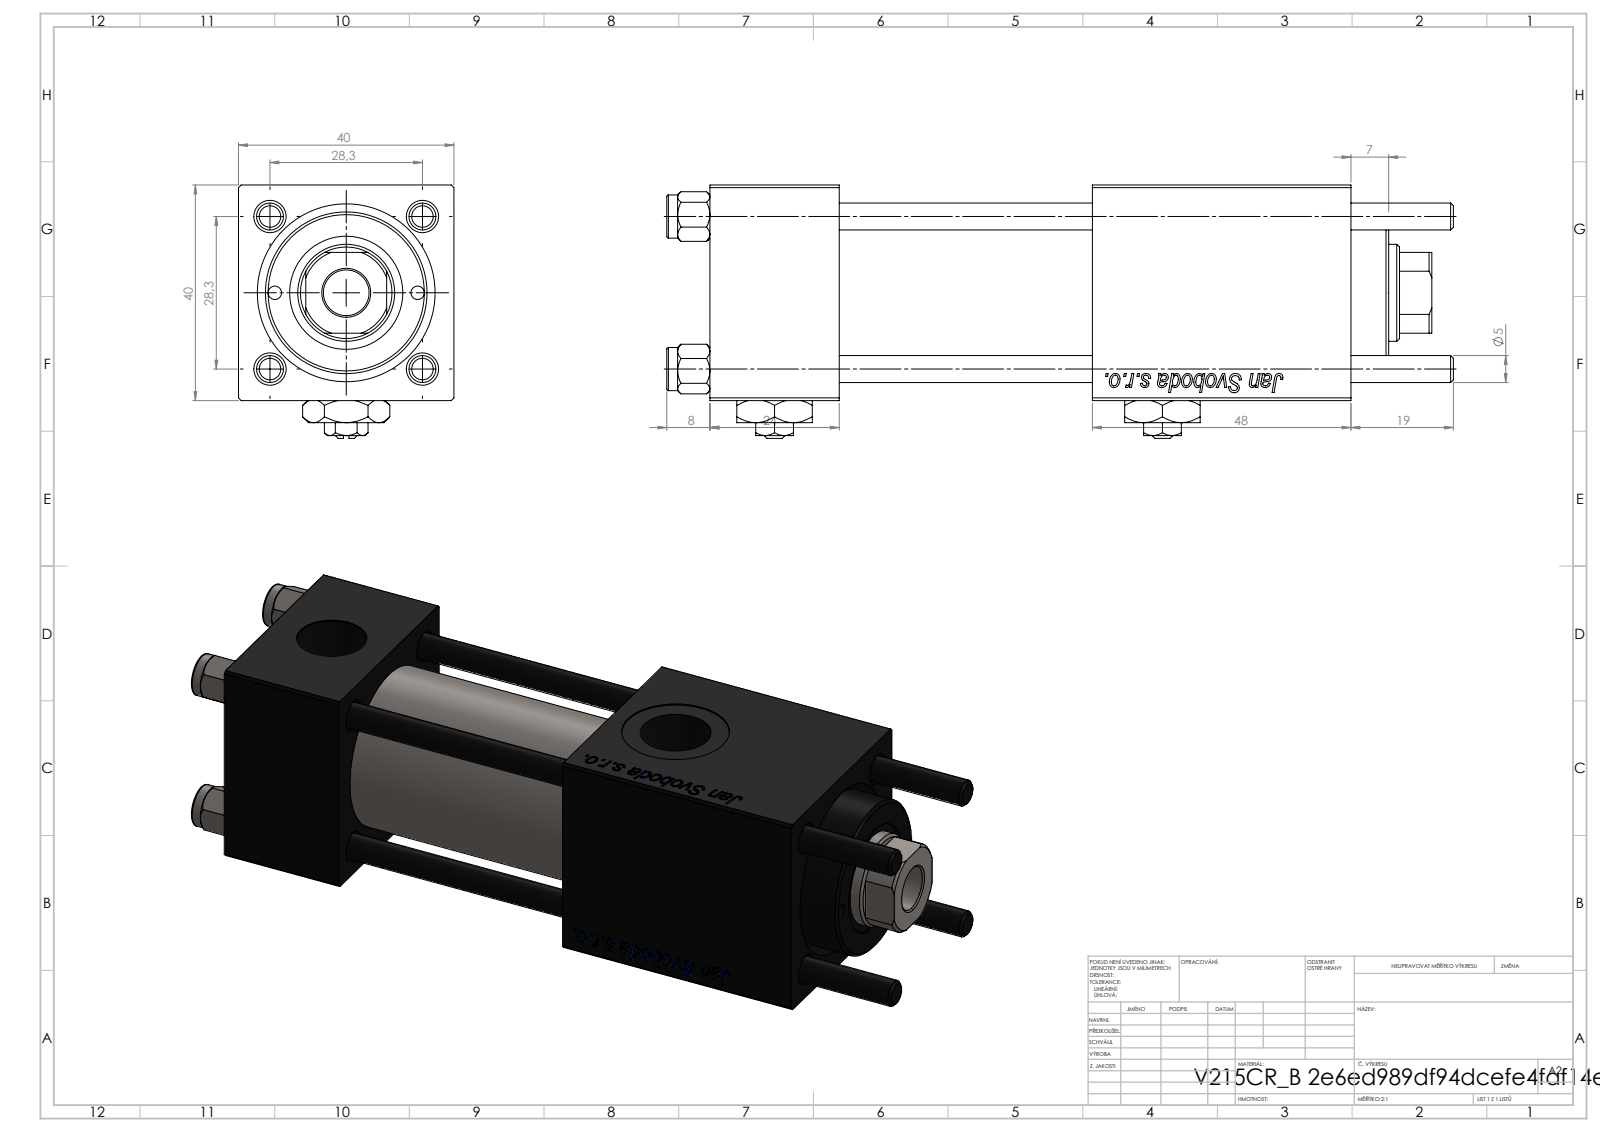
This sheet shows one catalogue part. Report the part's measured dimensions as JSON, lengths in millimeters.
{"part_name": "V215_VC_A; Zatka_pro_OIL_PORT; NUT_M5_B; V215CR_B-1 (+2 more)", "step_written_by": "SolidWorks 2019 (CONFIG_CONTROL_DESIGN)", "units": "millimeters", "bodies": {"solids": 13, "faces": 1259, "planar": 477, "cylindrical": 92, "other": 690}, "overall_size": [146, 47, 40], "volume_mm3": 150607, "surface_area_mm2": 62908, "round_holes": [[5, 4], [20, 4], [13.16, 3], [2.5, 2], [7, 2], [8.5, 1], [13, 1], [18, 1], [21, 1], [25, 1], [30, 1]], "round_bosses_or_shafts": [[8, 4], [31, 1]], "partial_cylinders_radius": [[8.5, 1]], "face_to_face_distances": [40, 24, 47, 71, 39.8, 90.3, 66.3, 19.3, 119, 95], "hole_center_spacings": [14.18, 20.01, 28.3, 30.84, 13.25, 40.02, 26.5, 72]}
